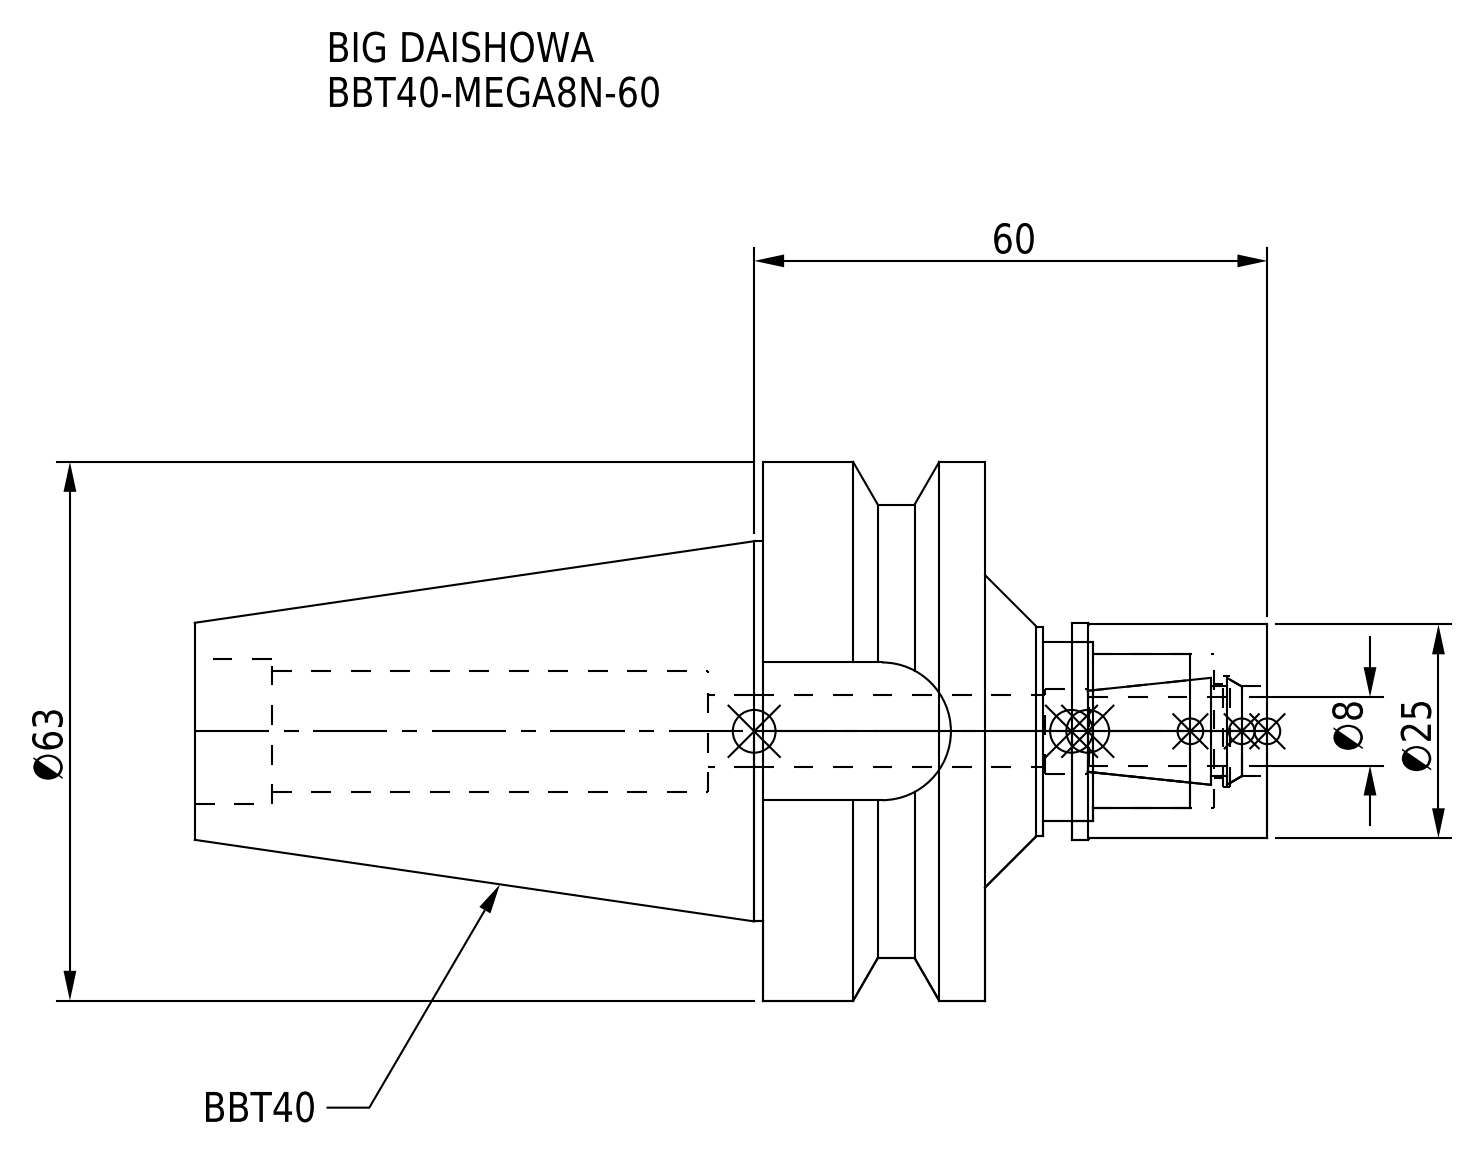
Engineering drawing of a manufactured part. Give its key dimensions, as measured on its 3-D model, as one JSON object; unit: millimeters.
{"part_name": "BBT40-MEGA8N-60; DXF_TEMP_ASSY_ASM_4_ASM.stp; MGN8_1.stp; BBT40-MEGA8N-60_1.stp (+3 more)", "step_written_by": "SolidWorks 2019 (CONFIG_CONTROL_DESIGN)", "units": "millimeters", "bodies": {"solids": 2, "faces": 76, "planar": 22, "cylindrical": 40, "other": 14}, "overall_size": [125.4, 63, 63], "volume_mm3": 137702, "surface_area_mm2": 28225, "round_holes": [[8.4, 1], [8.41, 1], [10, 1], [10.5, 1], [11, 1], [13, 1], [14.2, 1], [17, 1], [18, 1], [21, 1]], "round_bosses_or_shafts": [[63, 1], [53, 1], [44.45, 1], [25.3, 1], [25, 1], [24.5, 1]], "partial_cylinders_radius": [[8.05, 1]], "face_to_face_distances": [26, 45, 33, 59, 125.4, 92.4, 66.4, 9, 116.4, 16.1]}
